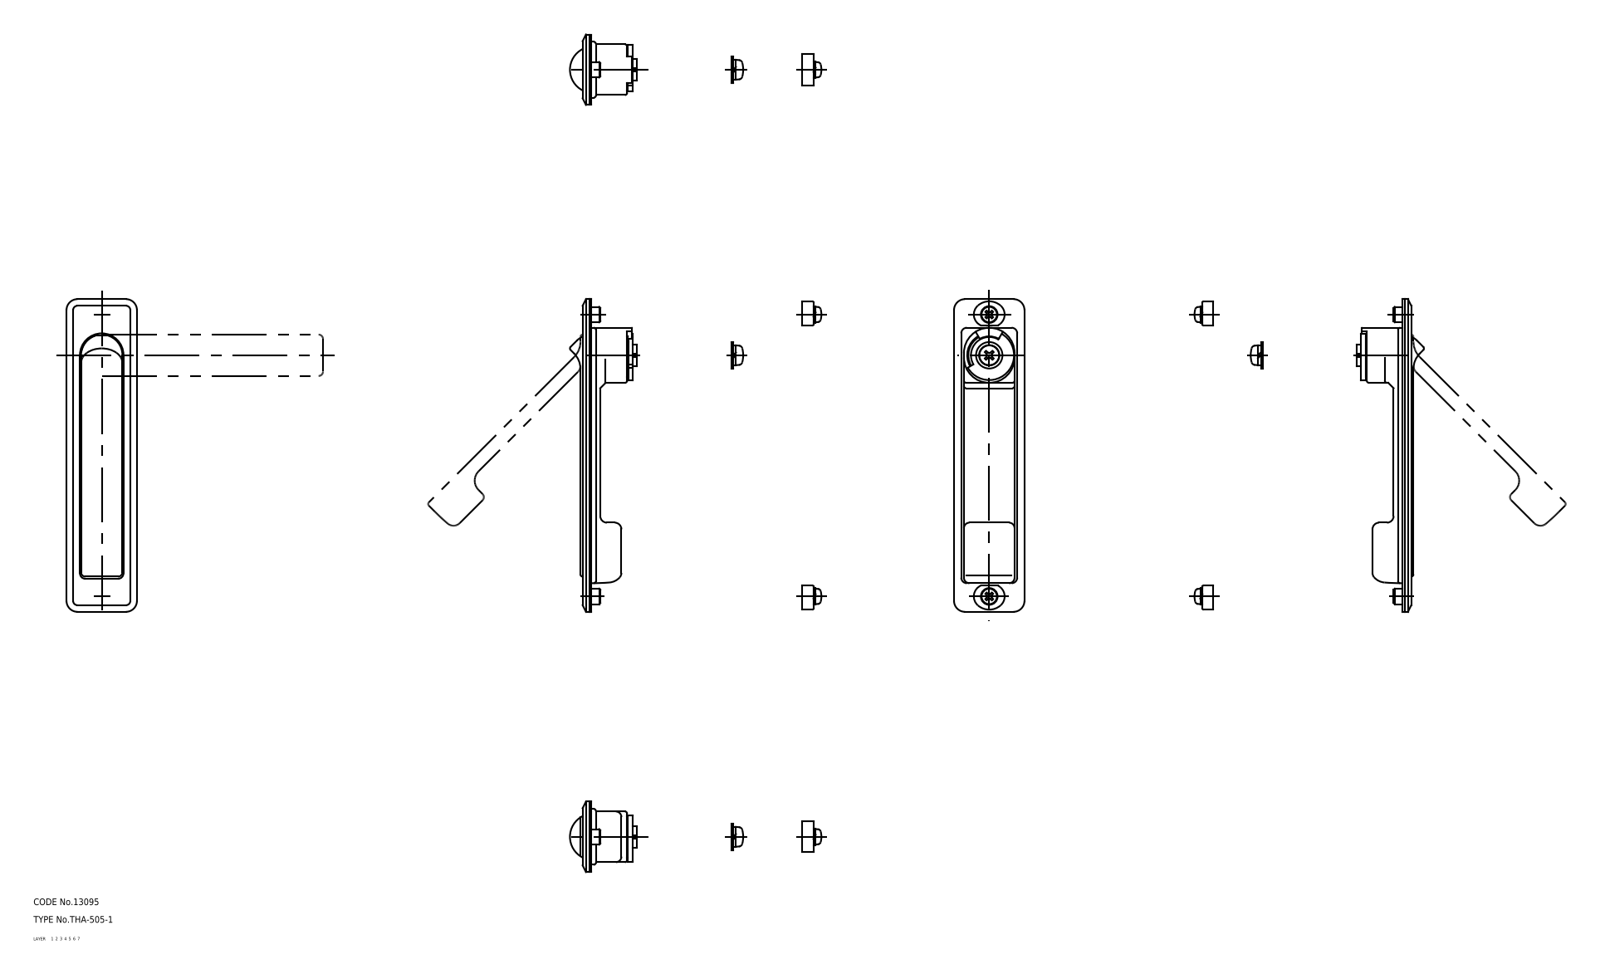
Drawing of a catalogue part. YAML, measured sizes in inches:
part_name: "bracket; screw_B; shaft; screw_A (+6 more)"
step_written_by: "CADfix (AUTOMOTIVE_DESIGN)"
units: inches
bodies: {solids: 11, faces: 391, planar: 0, cylindrical: 0, other: 391}
overall_size: [5.591, 1.411, 1.26]
volume: 2.363
surface_area: 46.48
